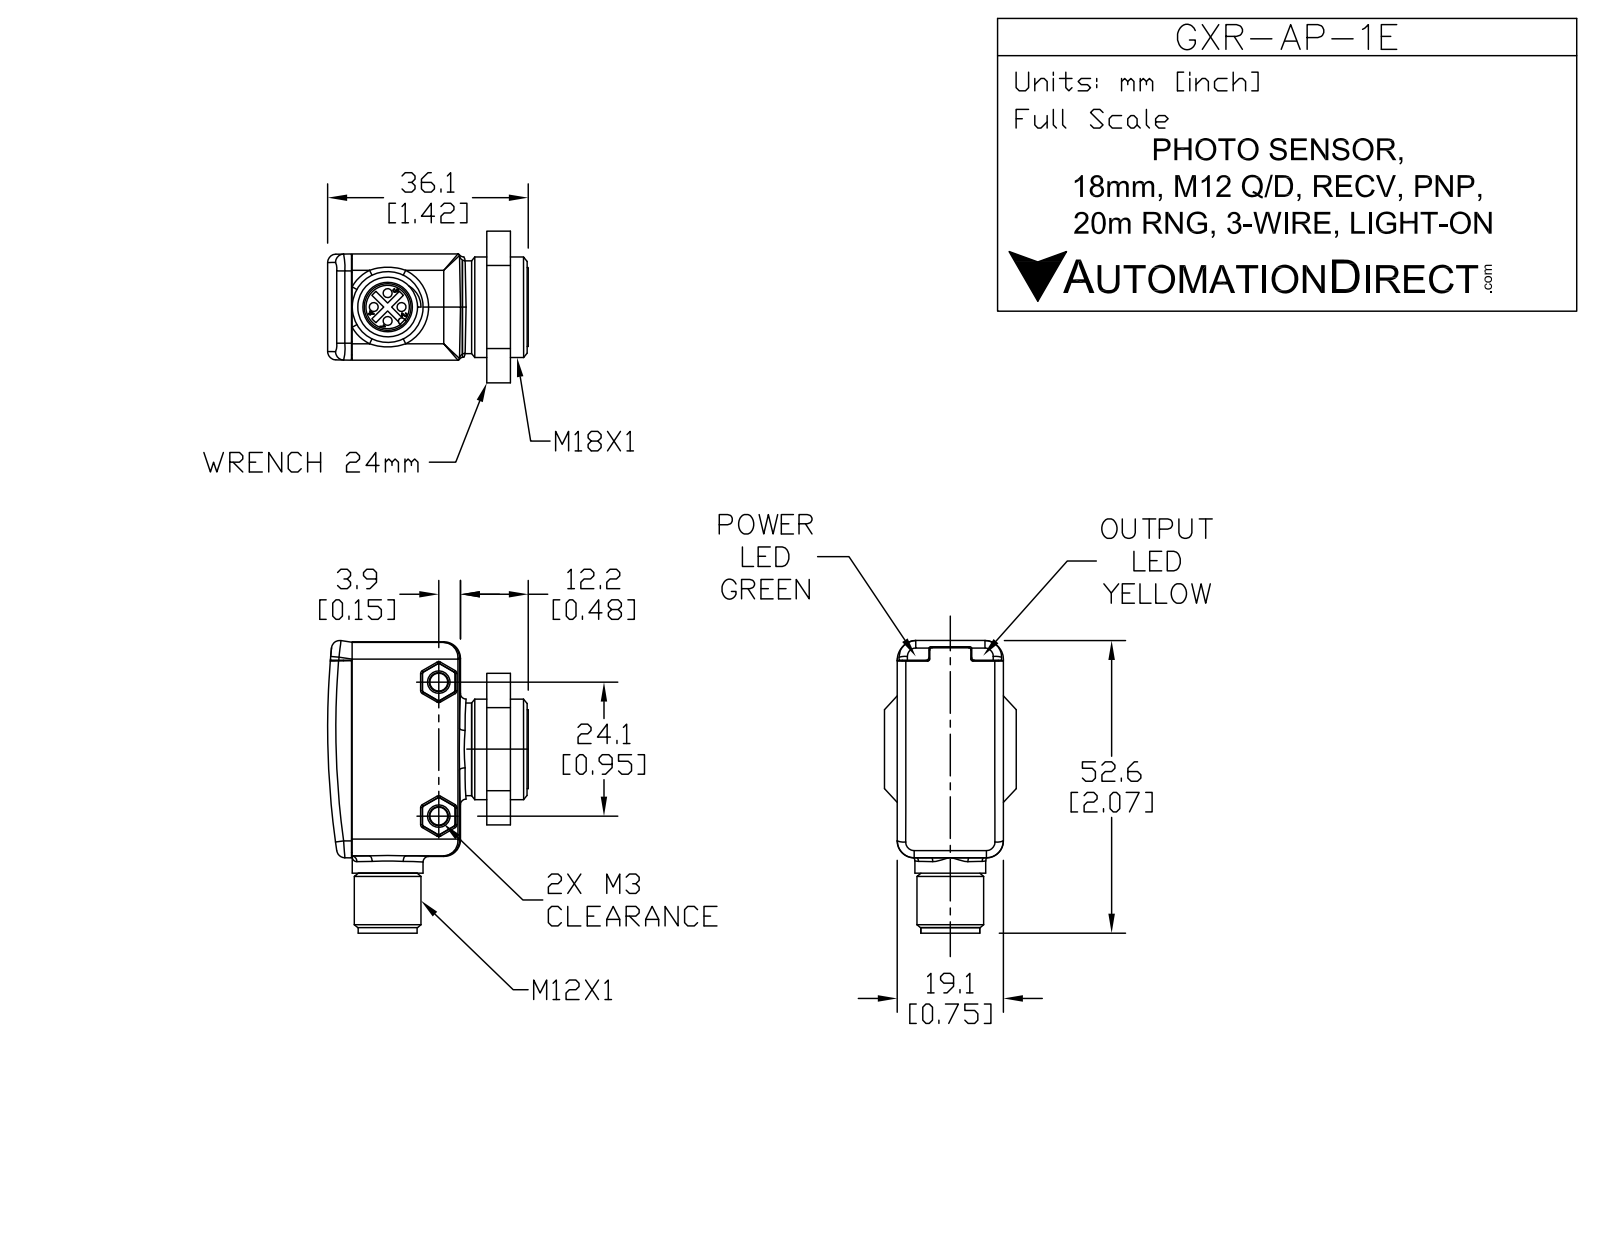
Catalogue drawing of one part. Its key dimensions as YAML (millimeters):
part_name: "GXR-AP-1E"
step_written_by: "SolidWorks 2013 (AUTOMOTIVE_DESIGN)"
units: millimeters
bodies: {solids: 1, faces: 107, planar: 60, cylindrical: 33, other: 14}
overall_size: [52.66, 36.1, 23.85]
volume: 21253
surface_area: 6452
round_holes:
  - {diameter: 3.2, count: 2}
  - {diameter: 8.36, count: 1}
round_bosses_or_shafts:
  - {diameter: 18, count: 1}
  - {diameter: 17.5, count: 1}
  - {diameter: 14.2, count: 1}
  - {diameter: 12.68, count: 1}
  - {diameter: 11.55, count: 1}
  - {diameter: 10.6, count: 1}
partial_cylinders:
  - {radius: 1.5, count: 8}
  - {radius: 1, count: 4}
  - {radius: 139.57, count: 1}
face_to_face_distances: [19.1, 7.2, 2.12, 9.32, 19.2, 5, 2.88, 12.2, 38.8, 5.95]
hole_center_spacings: [24.1]
